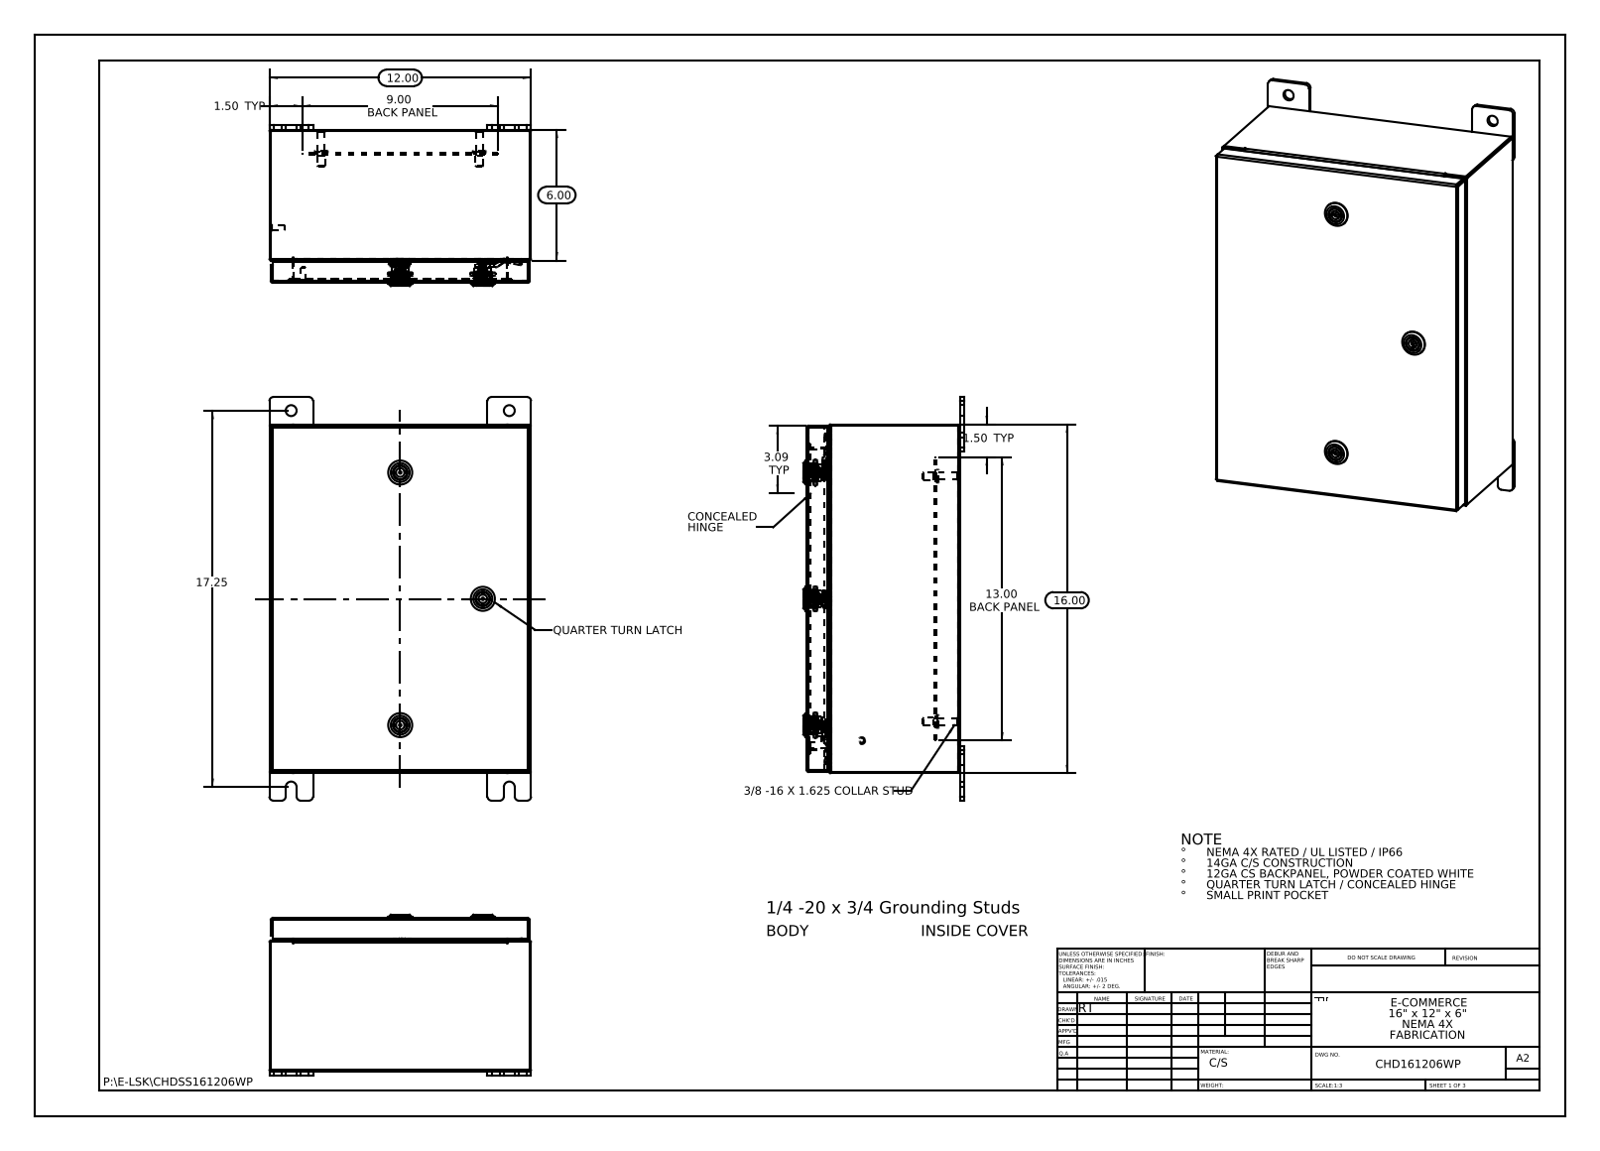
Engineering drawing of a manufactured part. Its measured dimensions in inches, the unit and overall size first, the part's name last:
Units: inches
Overall size (bounding box): 18.5 × 12 × 7.366
Round holes (diameter × count): ⌀0.5 ×8, ⌀0.197 ×3, ⌀0.394 ×3, ⌀0.4 ×3, ⌀0.63 ×3, ⌀0.787 ×3
Round bosses / shafts (diameter × count): ⌀0.236 ×5, ⌀0.625 ×4, ⌀0.375 ×4, ⌀0.33 ×4, ⌀1.102 ×3, ⌀0.78 ×3, ⌀0.626 ×3, ⌀0.61 ×3
Partial cylindrical surfaces — rounded edges, fillets, slot ends (radius × count): R0.006 ×99, R0.118 ×99, R0.028 ×36, R0.19 ×24, R0.013 ×18, R0.088 ×18, R0.02 ×12, R0.197 ×12
Main face-to-face distances: 0.075, 0.074, 11.925, 7.02, 6.945, 6.946, 6.871, 15.925, 1, 1.075
Hole centre spacings: 11.975, 2.225, 3.3, 3.628, 3.629, 5.246, 5.628, 5.749
Volume: 81.88 in³ · Surface area: 2 060 in²
Bodies: 33 solids, 2858 faces (870 planar, 890 cylindrical, 1098 other)
Part name (STEP PRODUCT): CHDSS161206WP Top; CHD161206WP; Quarter-20 CD Stud; Housing-211301-IB-Industrilas_Housing-211301-IB-Industrilas (+8 more)
STEP written by: SolidWorks 2013 (CONFIG_CONTROL_DESIGN)
